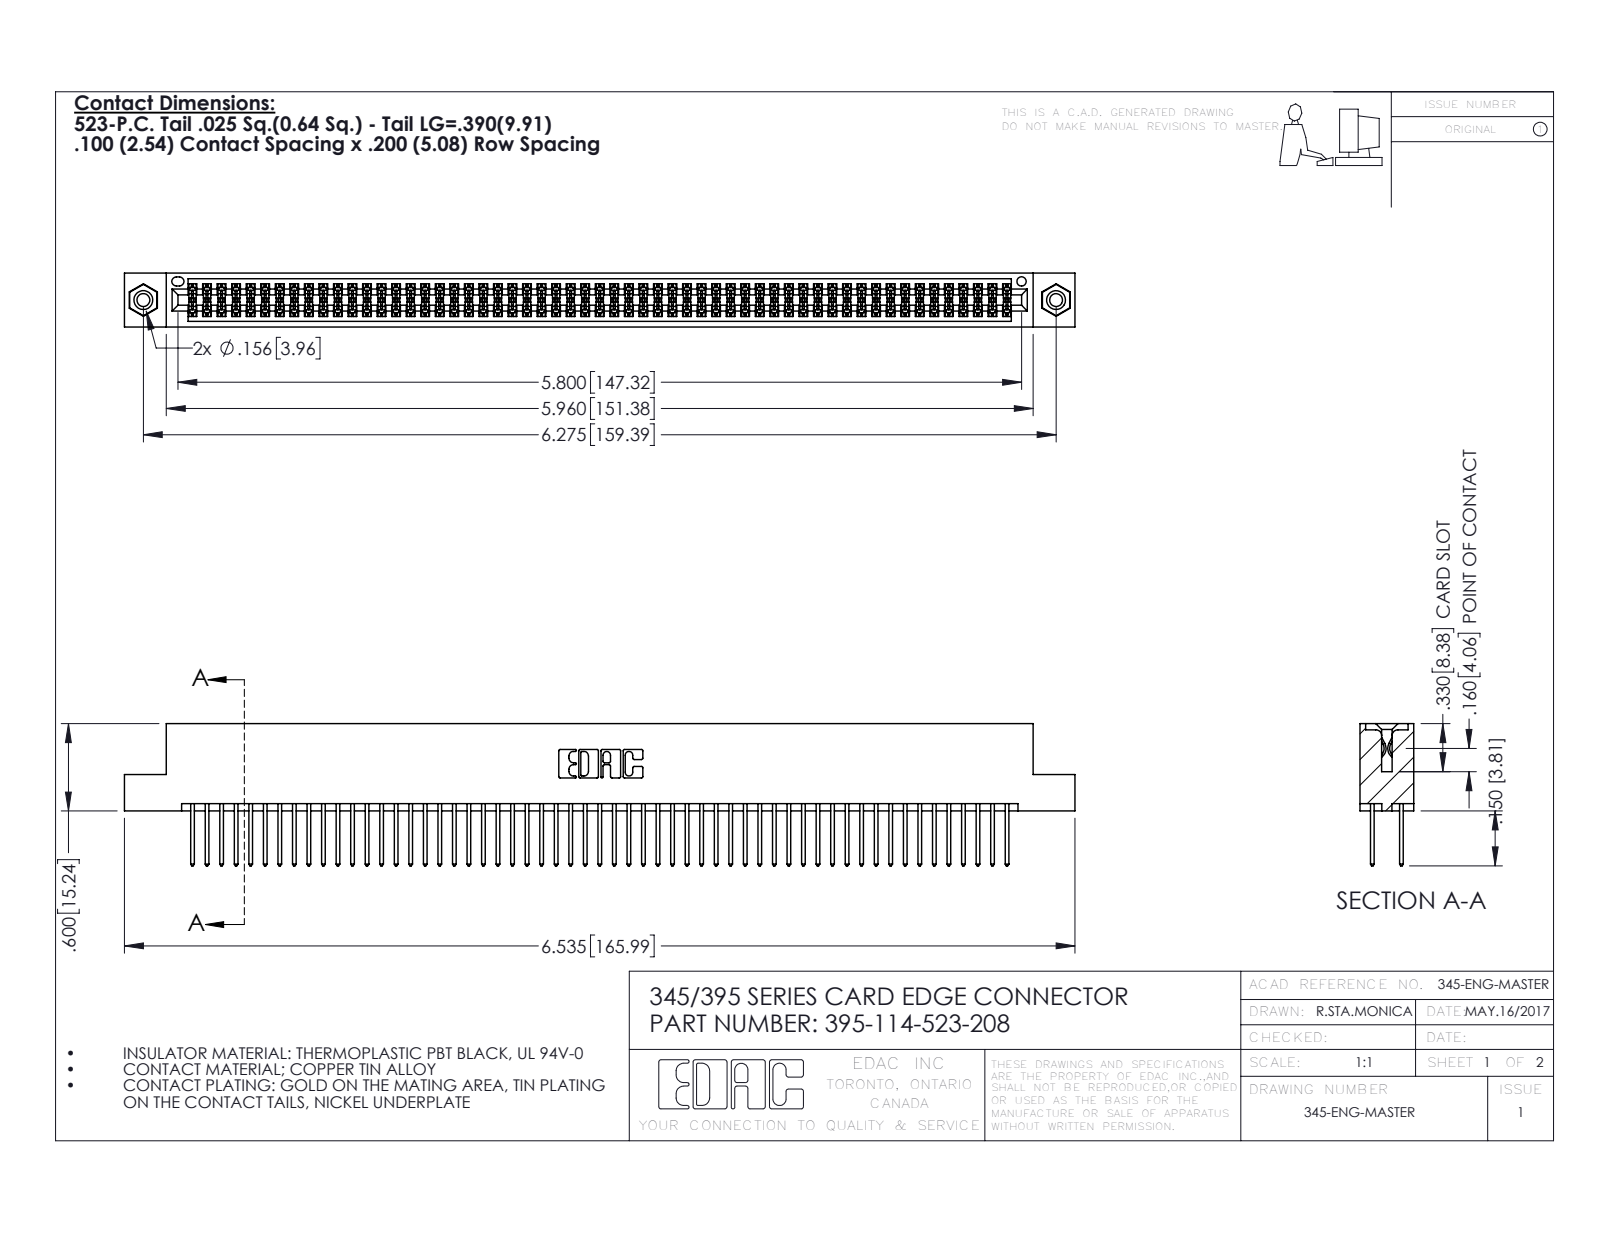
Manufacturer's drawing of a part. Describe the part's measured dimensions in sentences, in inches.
The part is named "345 Part_Flush Mounting Lugs - 0.156 Dia-TI; 345-250-001_345-250-003-102; 395-114-523-208; 345-292-001_345-293-123". Its 3-D file was written by "SolidWorks 2016 (CONFIG_CONTROL_DESIGN)". It is 117 solids with 5886 faces: 3874 planar, 1996 cylindrical and 16 other. Overall it measures 6.535 by 0.977 by 0.37 inches. Its volume is 1.006 cubic inches and its surface area 39.88 square inches. Round holes: 2 of diameter 0.089, 2 of diameter 0.125, 2 of diameter 0.156, 1 of diameter 0.064. Round bosses or shafts: 2 of diameter 0.155. Partial cylindrical surfaces (rounded edges, fillets, slot ends): 171 of radius 0.006, 114 of radius 0.01, 22 of radius 0.01, 6 of radius 0.007, 6 of radius 0.031, 3 of radius 0.026, 2 of radius 0.014, 2 of radius 0.019. The main face-to-face distances are 0.072, 0.298, 0.2, 0.098, 0.272, 0.025, 0.37, 0.225, 0.175, 0.149. The hole center spacings are 0.27, 6.039, 6.275.
